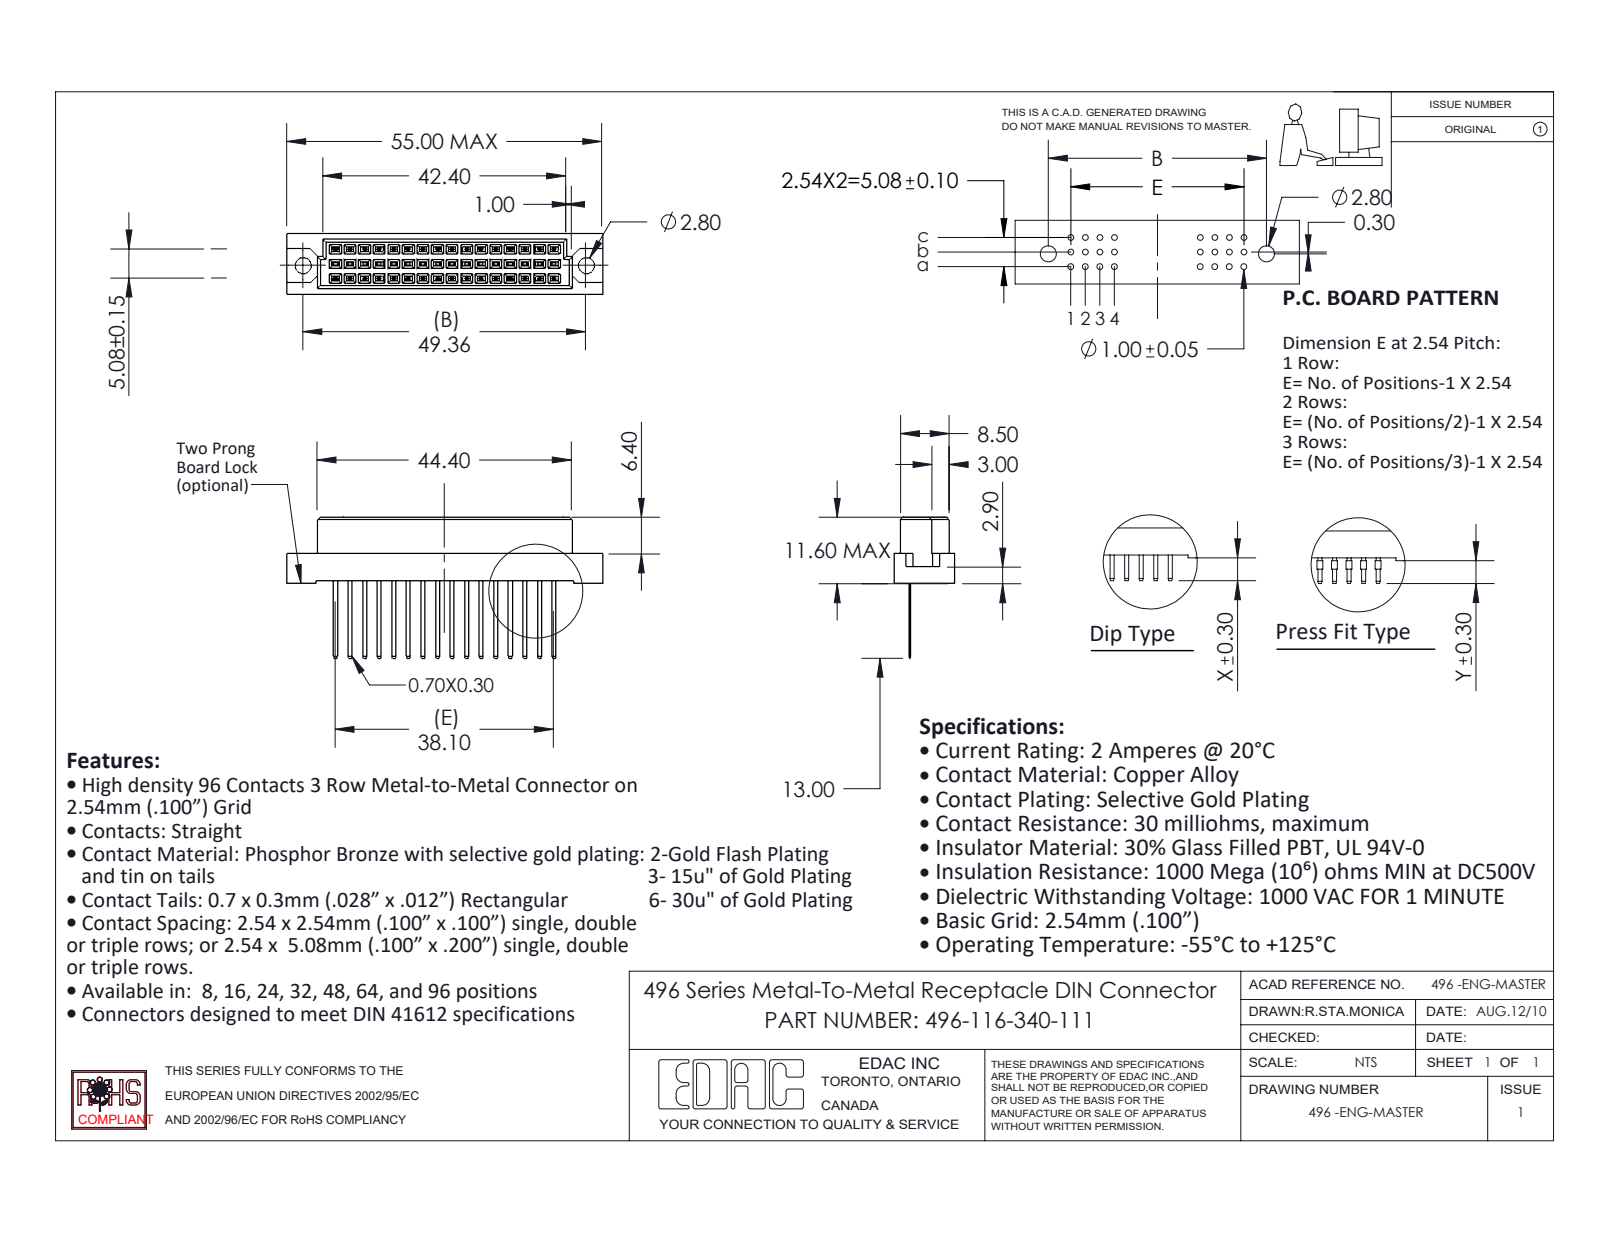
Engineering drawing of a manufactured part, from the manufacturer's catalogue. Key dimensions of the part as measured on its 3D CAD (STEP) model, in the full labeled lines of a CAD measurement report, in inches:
Part name (STEP PRODUCT): 496 Part_48; 496-290_40; 496-116-340-111
STEP written by: SolidWorks 2020 (CONFIG_CONTROL_DESIGN)
Units: inches
Bodies: 17 solids, 826 faces (822 planar, 4 cylindrical, 0 other)
Overall size (bounding box): 2.165 × 0.969 × 0.417
Volume: 0.284 in³ · Surface area: 7.401 in²
Round holes (diameter × count): ⌀0.11 ×2
Main face-to-face distances: 0.1, 0.2, 0.041, 0.376, 0.032, 0.103, 0.115, 0.303, 0.315, 0.061
Hole centre spacings: 1.943
